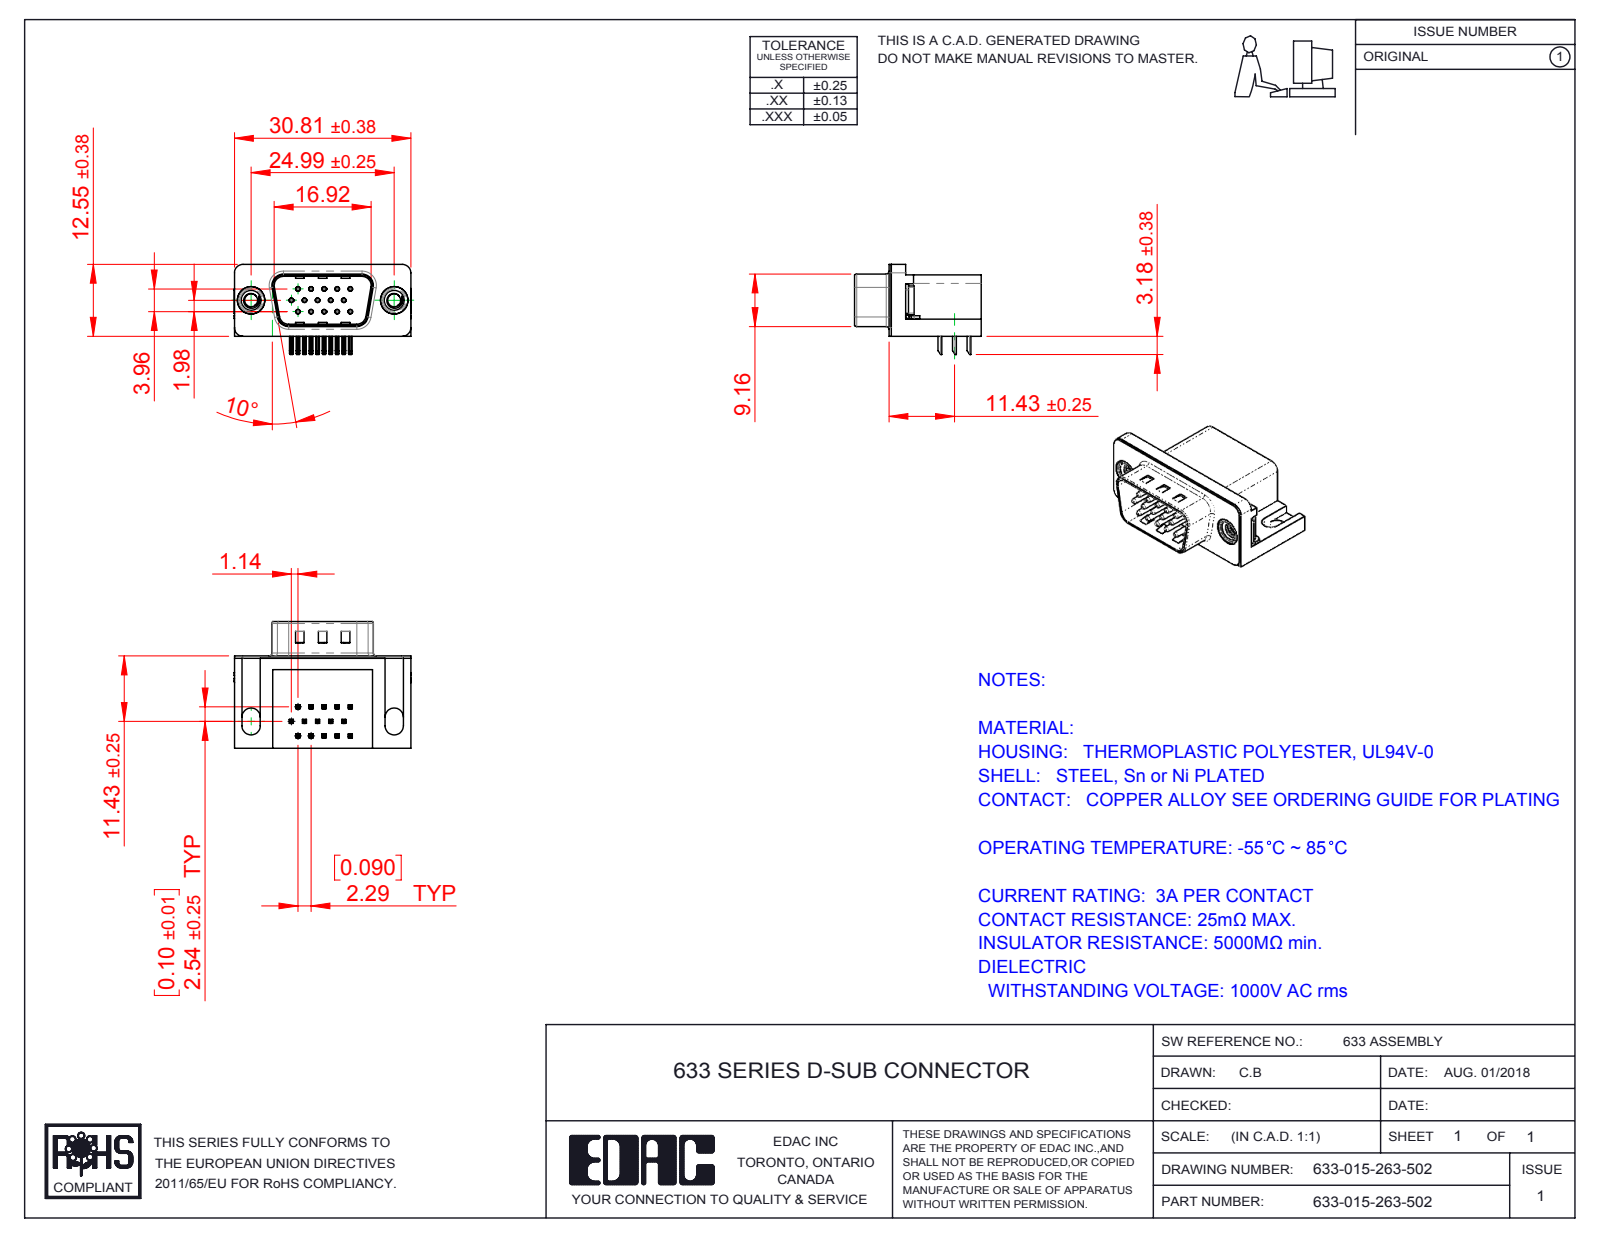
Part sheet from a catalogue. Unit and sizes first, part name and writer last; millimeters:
Units: millimetres
Overall size (bounding box): 30.89 × 22.1 × 15.73
Round holes (diameter × count): ⌀0.35 ×15, ⌀0.8 ×15, ⌀2.26 ×2, ⌀4 ×2, ⌀4.8 ×2, ⌀5 ×2
Round bosses / shafts (diameter × count): ⌀0.75 ×15, ⌀4.9 ×2, ⌀4.75 ×2, ⌀3.9 ×2
Partial cylindrical surfaces — rounded edges, fillets, slot ends (radius × count): R0.25 ×68, R0.12 ×30, R1 ×16, R0.5 ×9, R1.6 ×8, R1.5 ×7, R0.9 ×4, R2 ×4
Main face-to-face distances: 0.4, 10.35, 15.7, 2.9, 6.7, 16.1, 2.5, 0.35, 10.7, 13.2
Hole centre spacings: 3.96, 2.28, 4.57, 2.29, 6.05, 6.86, 7.92, 6.04
Volume: 4 027 mm³ · Surface area: 5 202 mm²
Bodies: 21 solids, 1439 faces (861 planar, 439 cylindrical, 139 other)
Part name (STEP PRODUCT): 633 Shell_15 Contact; 633 Housing_15 Contact; 633 Contact Top; 633-015-263-502 (+4 more)
STEP written by: SolidWorks 2016 (CONFIG_CONTROL_DESIGN)
